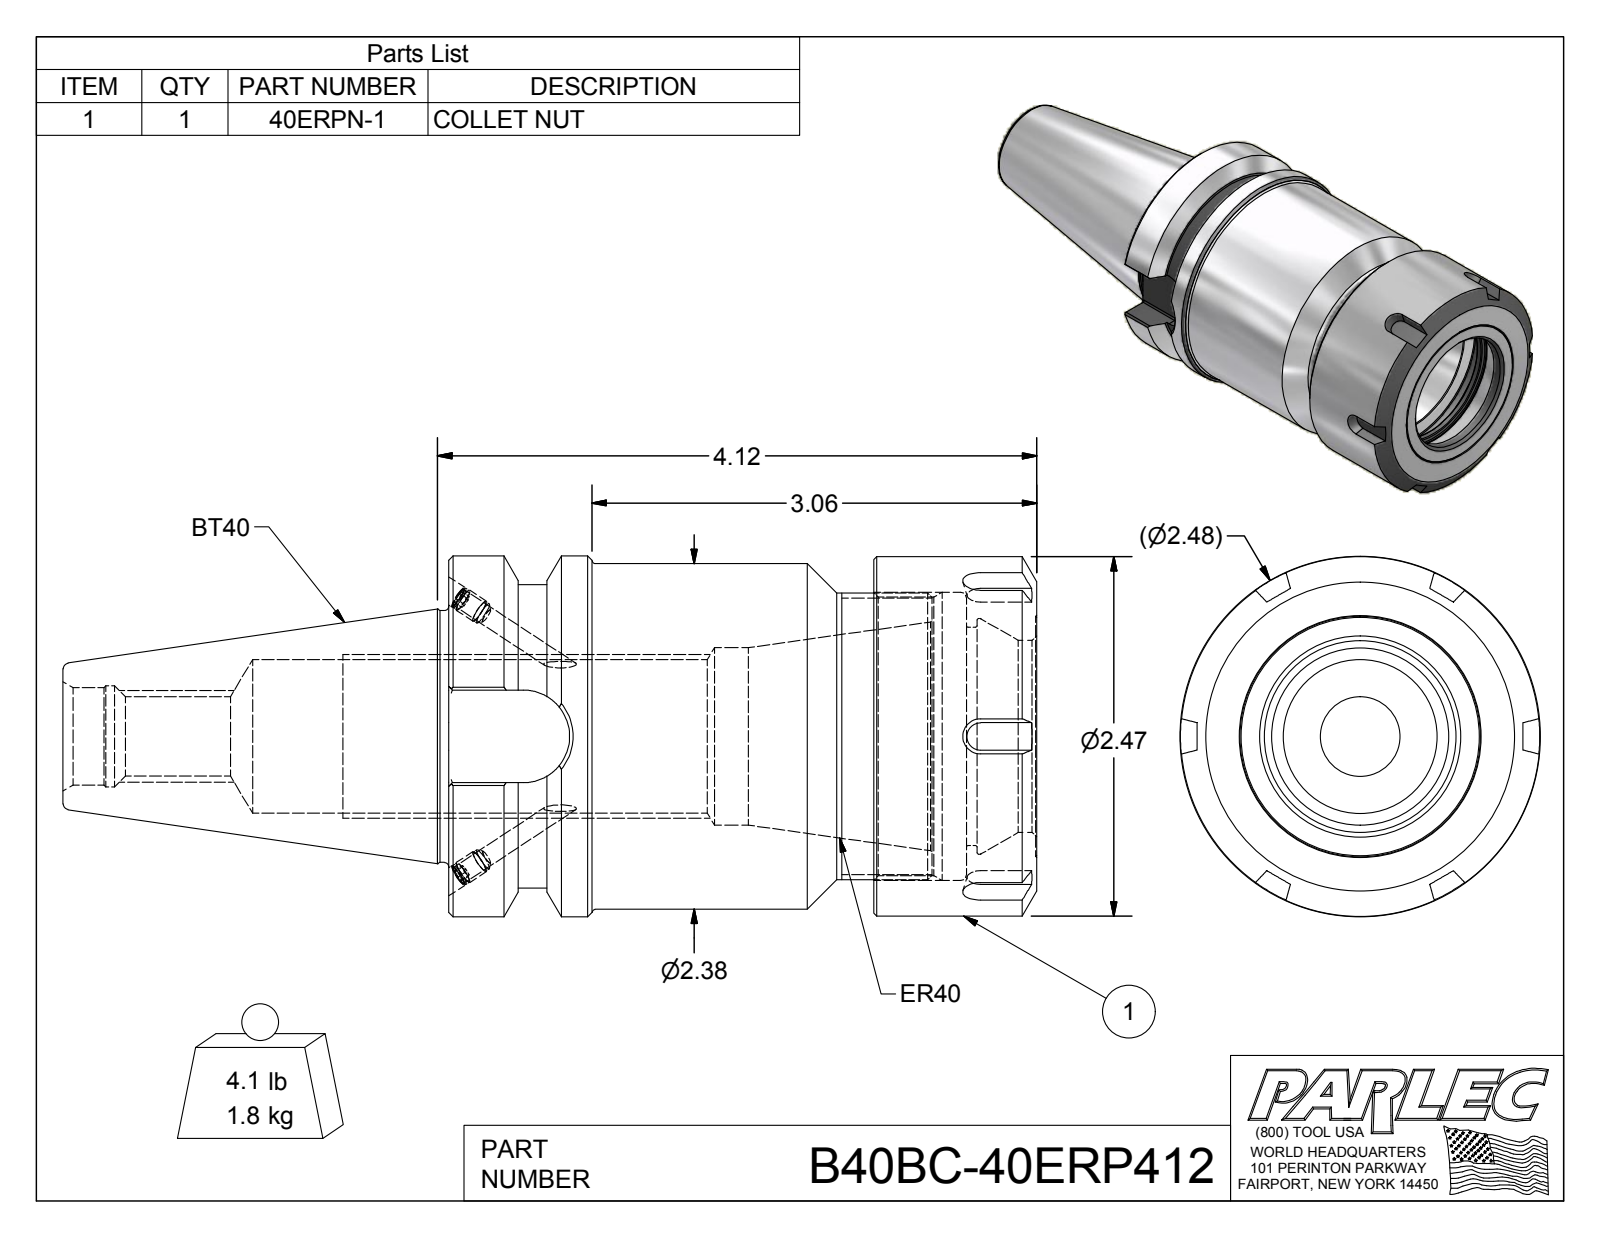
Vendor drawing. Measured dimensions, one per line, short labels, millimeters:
name: B40BC-40ERP412; B40BCB-40ER4-1; 029-965; 40ERPN
written by: Autodesk Inventor 2012 (AUTOMOTIVE_DESIGN)
unit: mm
bodies: 4 solids, 157 faces (68 planar, 39 cylindrical, 50 other)
size: 170.1 × 63 × 63
volume: 239 700 mm³; area: 54 450 mm²
holes: 2× ⌀3.3, 2× ⌀4.1, 1× ⌀13.8, 1× ⌀17, 1× ⌀17.6, 1× ⌀26.8, 1× ⌀31, 1× ⌀33.5, 1× ⌀38.1, 1× ⌀41.1, 1× ⌀48.7, 1× ⌀50.3
bosses: 2× ⌀4.2, 2× ⌀4, 1× ⌀63, 1× ⌀62.7, 1× ⌀60.3, 1× ⌀53, 1× ⌀50, 1× ⌀43.9
rounds: 8× R0.5, 1× R8.1
face distances: 102.7, 74.2, 28.4, 90.4, 16.2, 12.3, 84.4, 10.2, 6, 18.3
